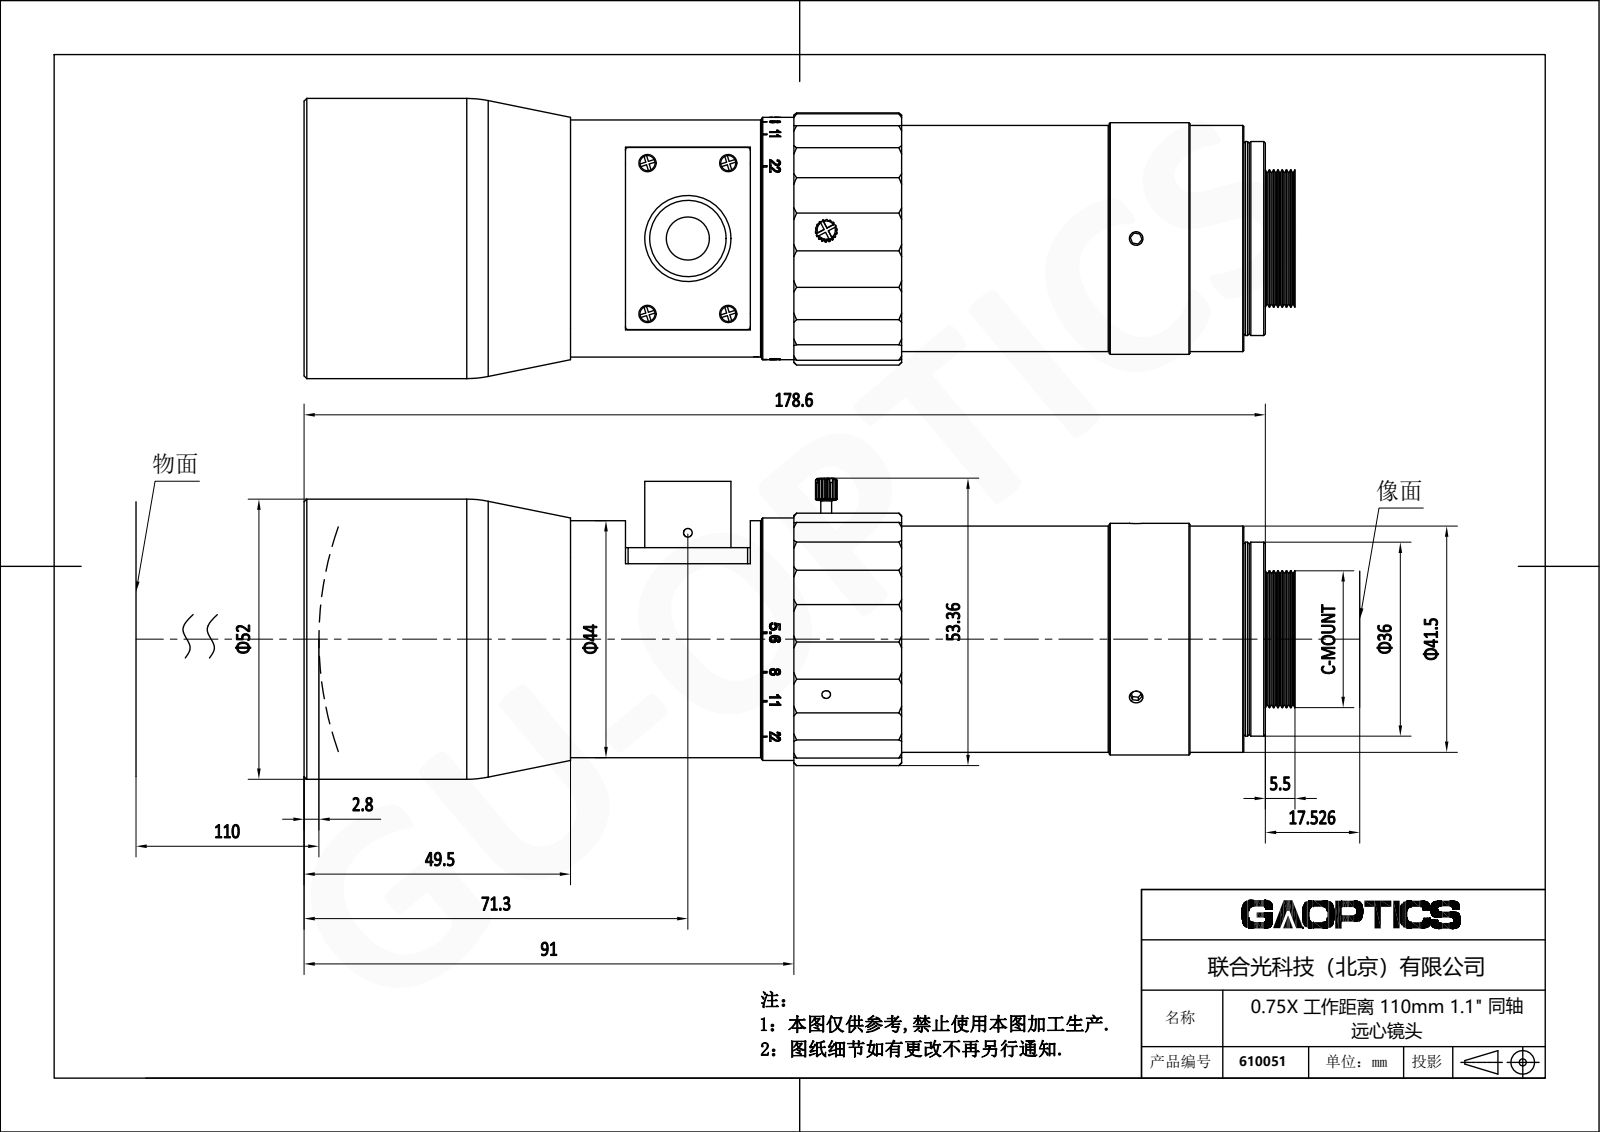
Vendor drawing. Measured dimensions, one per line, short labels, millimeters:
name: 610051
written by: SolidWorks 2019 (CONFIG_CONTROL_DESIGN)
unit: mm
bodies: 6 solids, 775 faces (0 planar, 0 cylindrical, 775 other)
size: 184.08 × 55.3 × 52
volume: 282 674 mm³; area: 34 808 mm²
